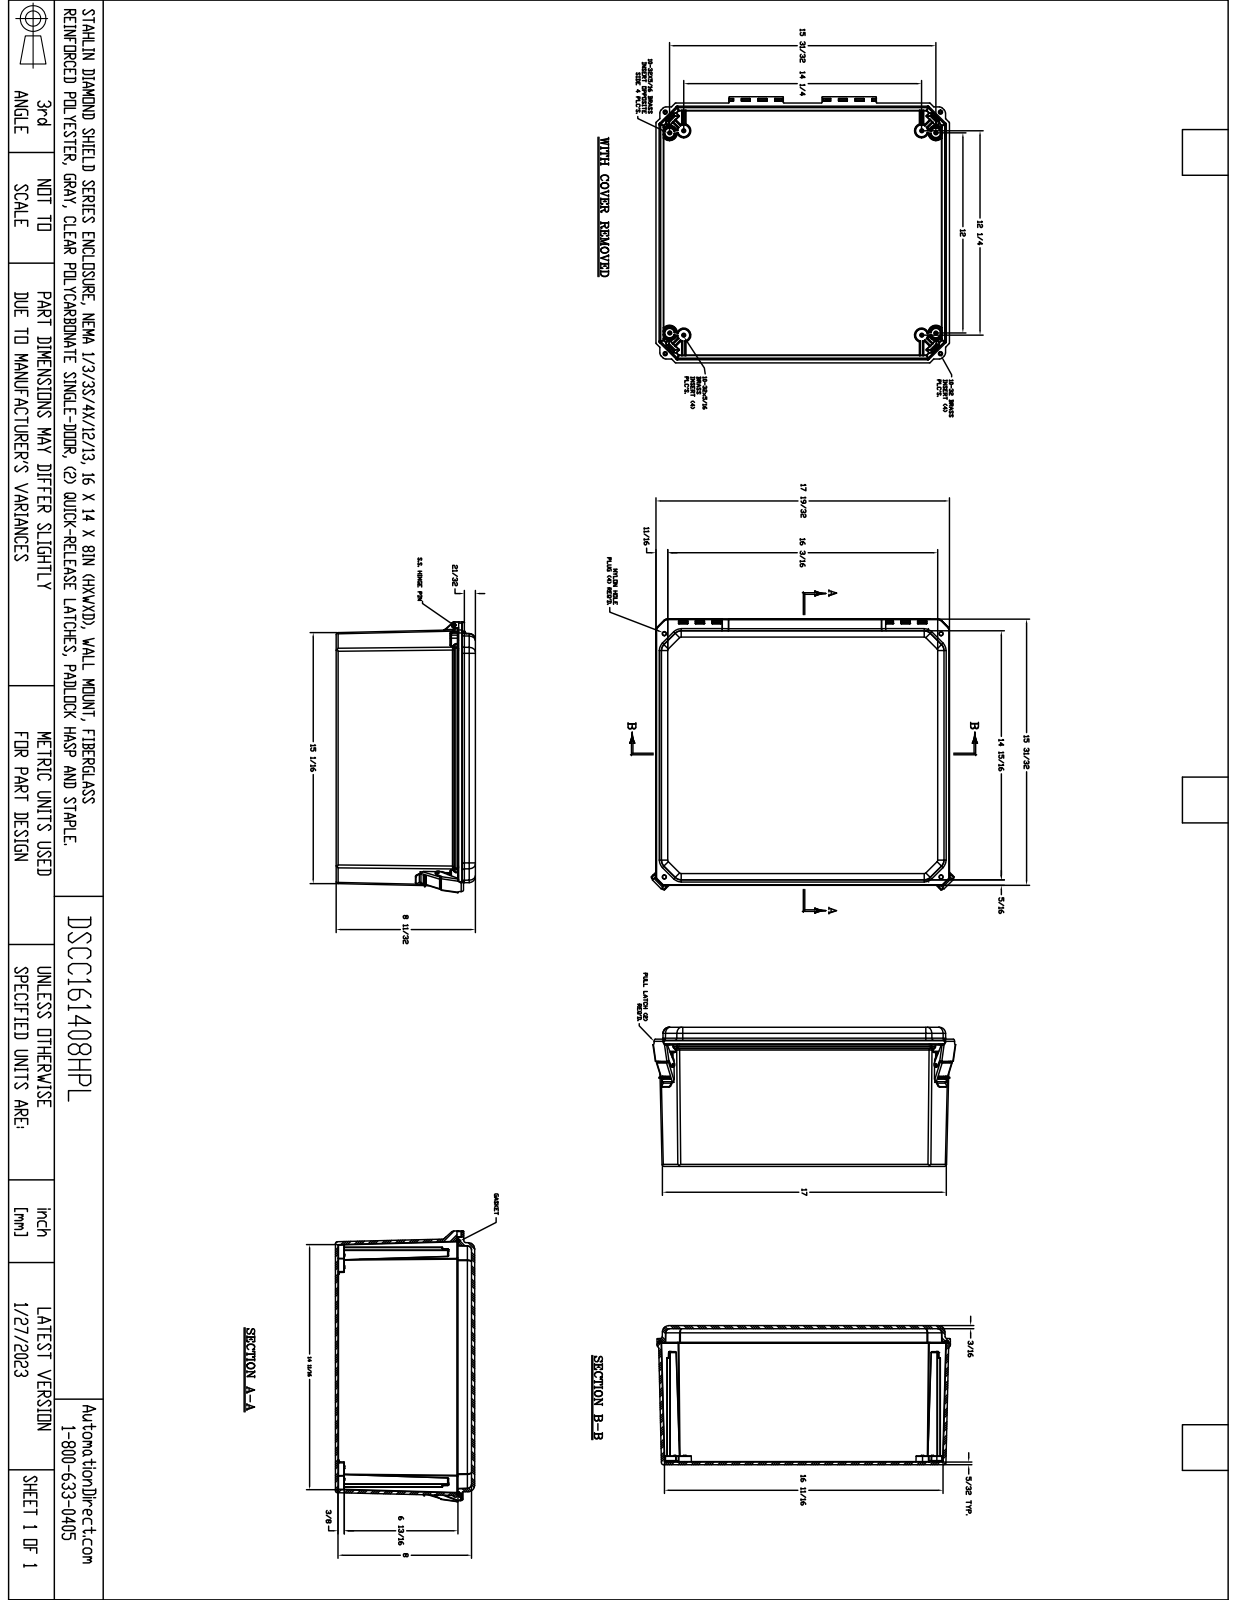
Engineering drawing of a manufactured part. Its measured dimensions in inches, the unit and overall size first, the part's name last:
Units: inches
Overall size (bounding box): 18.254 × 16.3 × 8.343
Round holes (diameter × count): ⌀0.156 ×12, ⌀0.135 ×10, ⌀0.152 ×8, ⌀0.15 ×4, ⌀0.219 ×4, ⌀0.252 ×4, ⌀0.312 ×4, ⌀0.137 ×1, ⌀0.375 ×1, ⌀0.375 ×1
Round bosses / shafts (diameter × count): ⌀0.246 ×12, ⌀0.3 ×4, ⌀0.209 ×4, ⌀0.135 ×1
Partial cylindrical surfaces — rounded edges, fillets, slot ends (radius × count): R0.01 ×202, R0.005 ×116, R0.02 ×59, R0.03 ×56, R0.125 ×29, R0.09 ×26, R0.03 ×24, R0.06 ×24
Main face-to-face distances: 0.156, 0.125, 8.218, 8.062, 8.343, 8.187, 0.18, 0.181, 0.125, 0.937
Hole centre spacings: 0.25, 15.461, 16.324, 16.584, 0.865, 15.106, 20.438, 1.33
Volume: 172.1 in³ · Surface area: 2 209 in²
Bodies: 29 solids, 2307 faces (702 planar, 924 cylindrical, 681 other)
Part name (STEP PRODUCT): FRCC161408HPL
STEP written by: SolidWorks 2018 (AUTOMOTIVE_DESIGN)
